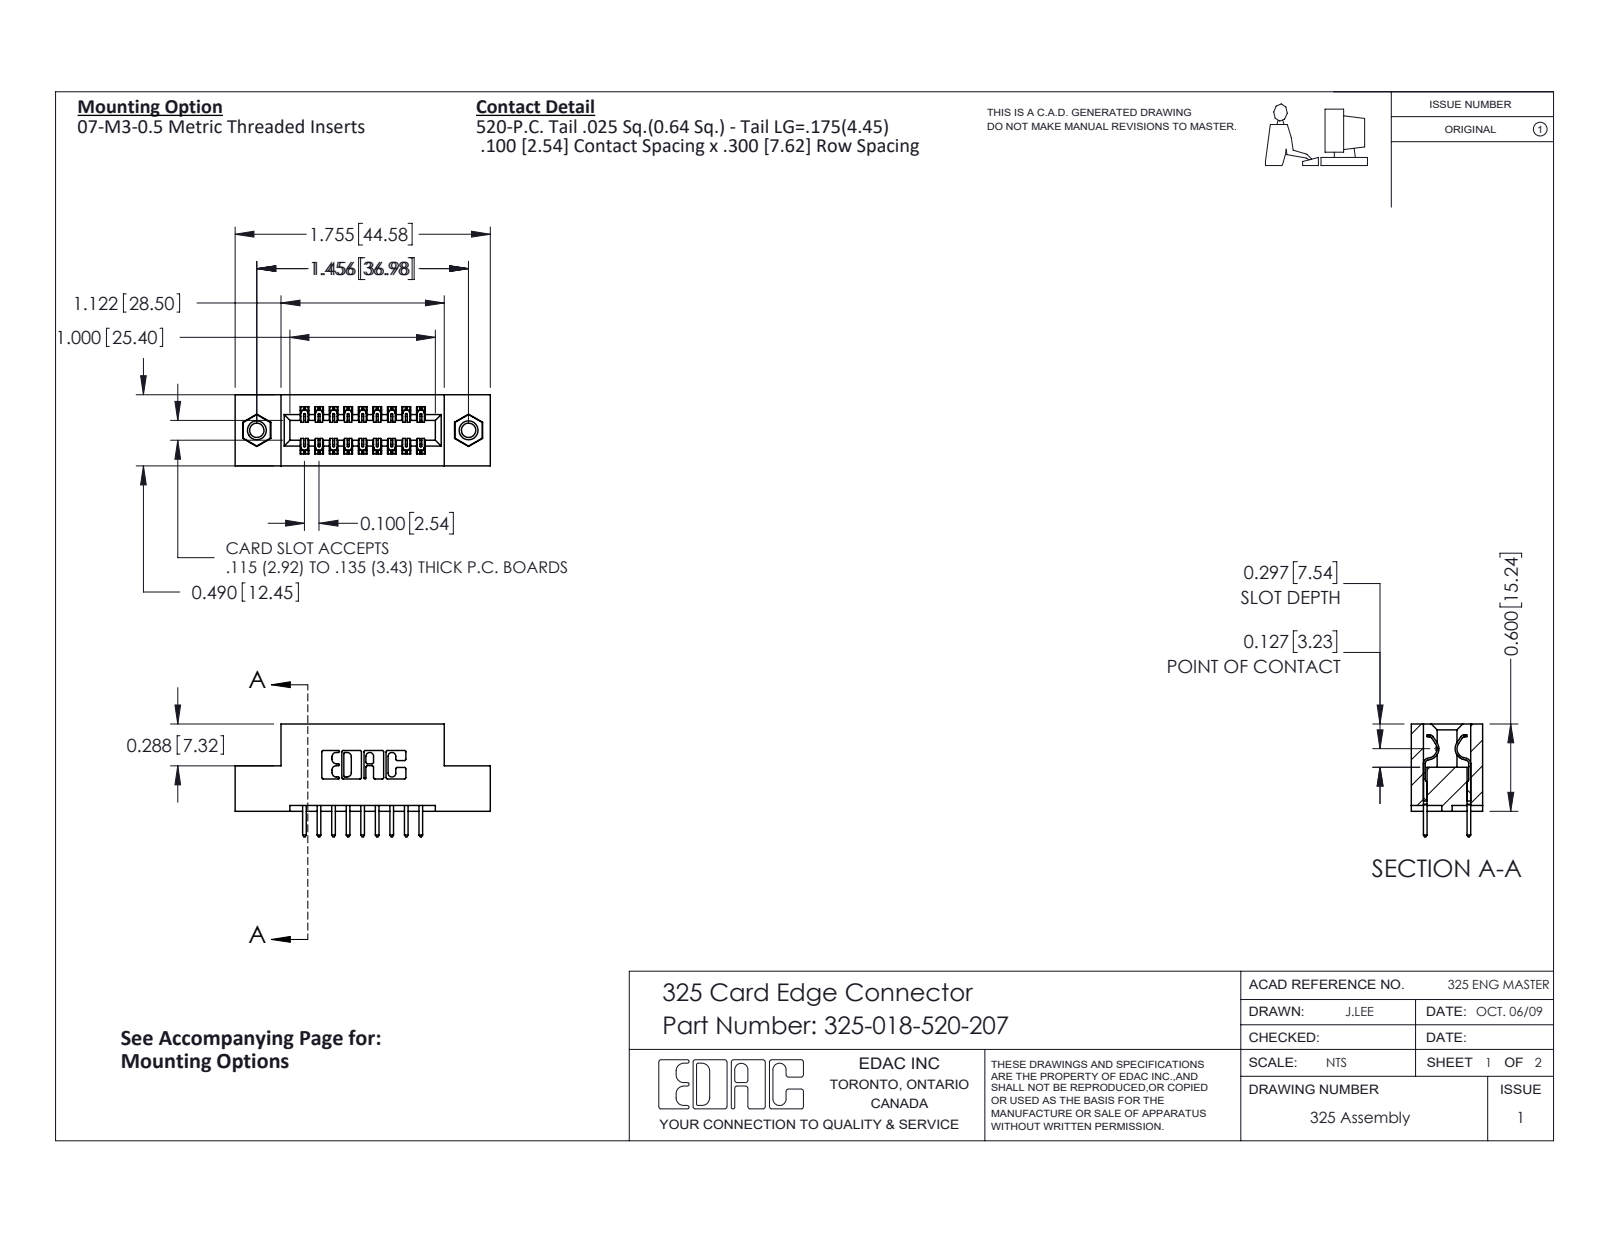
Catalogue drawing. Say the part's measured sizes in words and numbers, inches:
The part is named "325 Part_TI; 325-018-520-207; 345-250-001_345-250-005-103; 325-292-001_325-293-120". Its 3-D file was written by "SolidWorks 2016 (CONFIG_CONTROL_DESIGN)". It is 21 solids with 1110 faces: 750 planar, 344 cylindrical and 16 other. Overall it measures 1.755 by 0.775 by 0.49 inches. Its volume is 0.332 cubic inches and its surface area 8.982 square inches. Round holes: 2 of diameter 0.098, 2 of diameter 0.125, 2 of diameter 0.16. Round bosses or shafts: 2 of diameter 0.155. Partial cylindrical surfaces (rounded edges, fillets, slot ends): 27 of radius 0.006, 22 of radius 0.01, 18 of radius 0.01, 6 of radius 0.007, 6 of radius 0.031, 3 of radius 0.026, 2 of radius 0.014, 2 of radius 0.022. The main face-to-face distances are 0.3, 0.083, 0.407, 0.04, 0.1, 0.49, 0.2, 0.6, 0.4, 0.107. The hole center spacings are 1.456.
